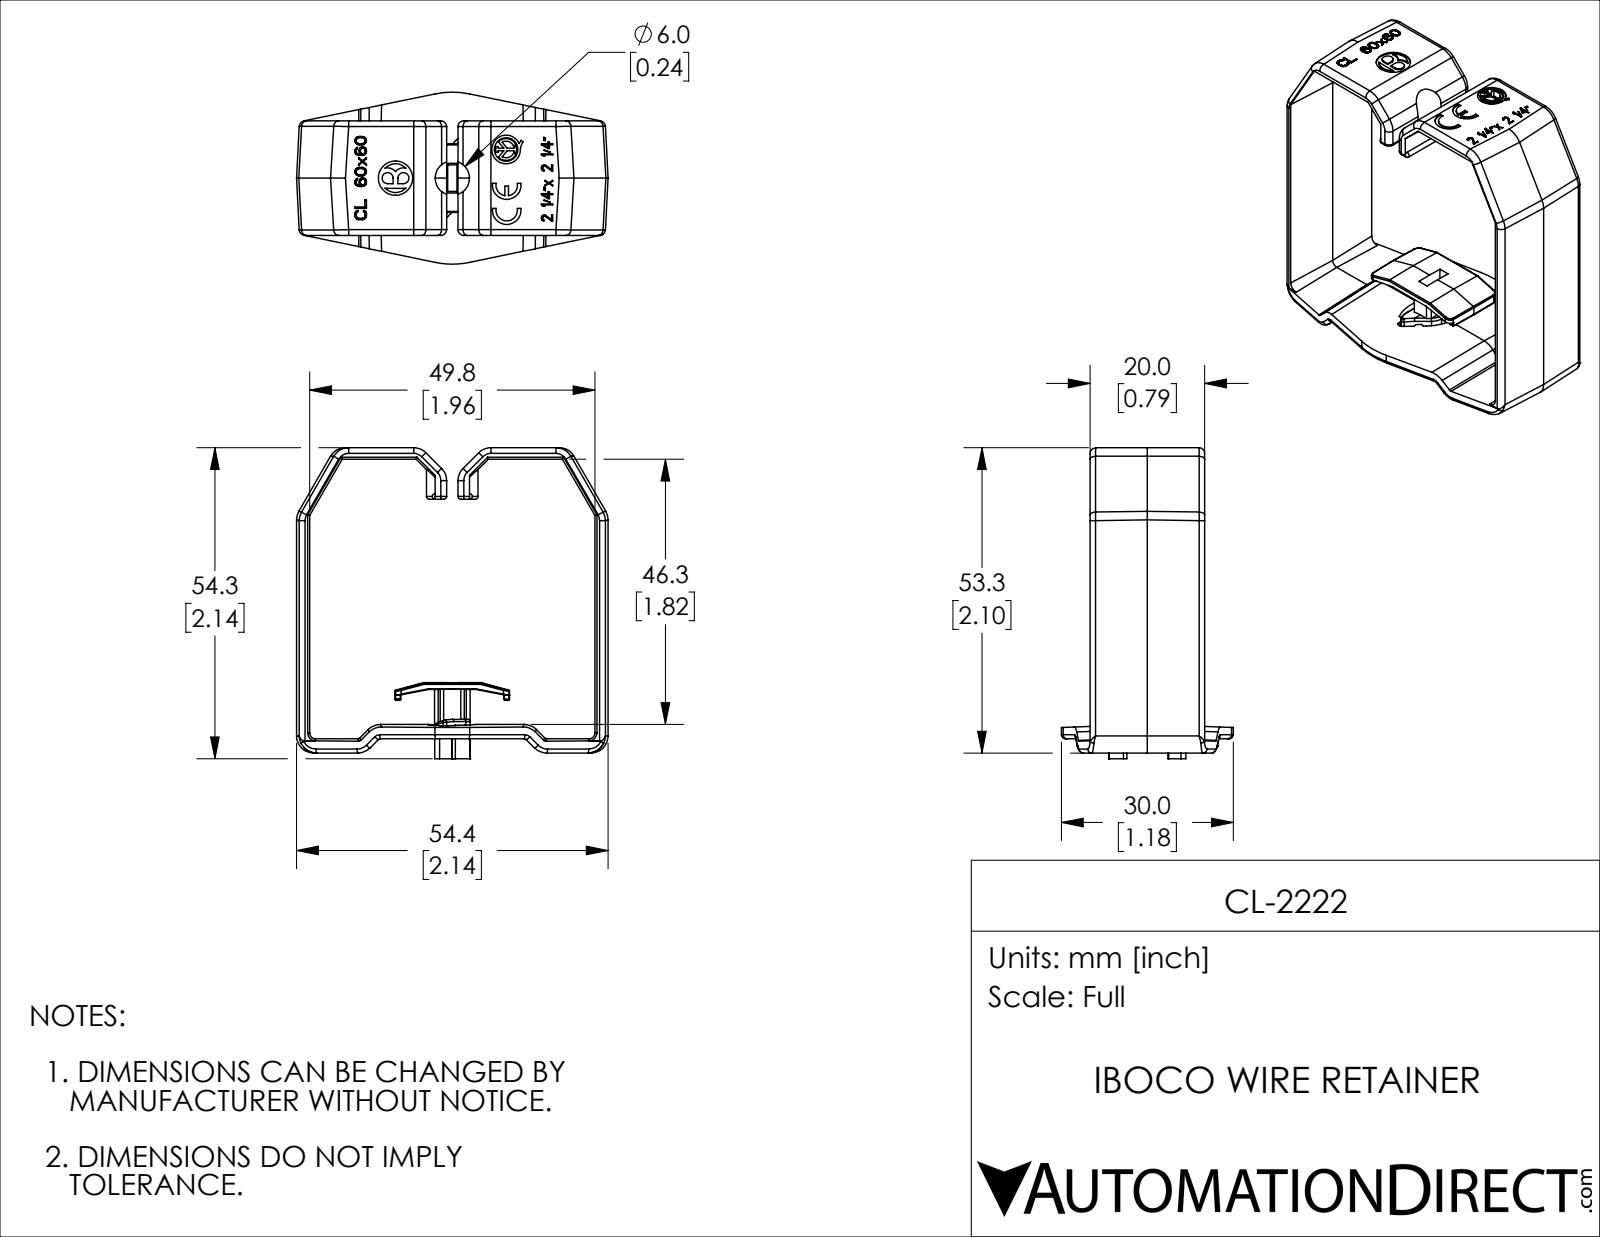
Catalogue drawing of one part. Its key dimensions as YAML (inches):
part_name: "CL-2222"
step_written_by: "SolidWorks 2019 (CONFIG_CONTROL_DESIGN)"
units: inches
bodies: {solids: 1, faces: 855, planar: 613, cylindrical: 180, other: 62}
overall_size: [2.142, 2.138, 1.181]
volume: 0.534
surface_area: 15.96
round_holes:
  - {diameter: 0.197, count: 1}
  - {diameter: 0.236, count: 1}
round_bosses_or_shafts:
  - {diameter: 0.161, count: 1}
partial_cylinders:
  - {radius: 0.039, count: 24}
  - {radius: 0.118, count: 23}
  - {radius: 0.008, count: 22}
  - {radius: 0.02, count: 18}
  - {radius: 0.028, count: 12}
  - {radius: 0.012, count: 6}
  - {radius: 0.016, count: 6}
  - {radius: 0.098, count: 4}
face_to_face_distances: [1.959, 2.139, 0.098, 1.821, 2, 1.919, 2.098, 0.079, 0.729, 0.039]
hole_center_spacings: [0.786]
